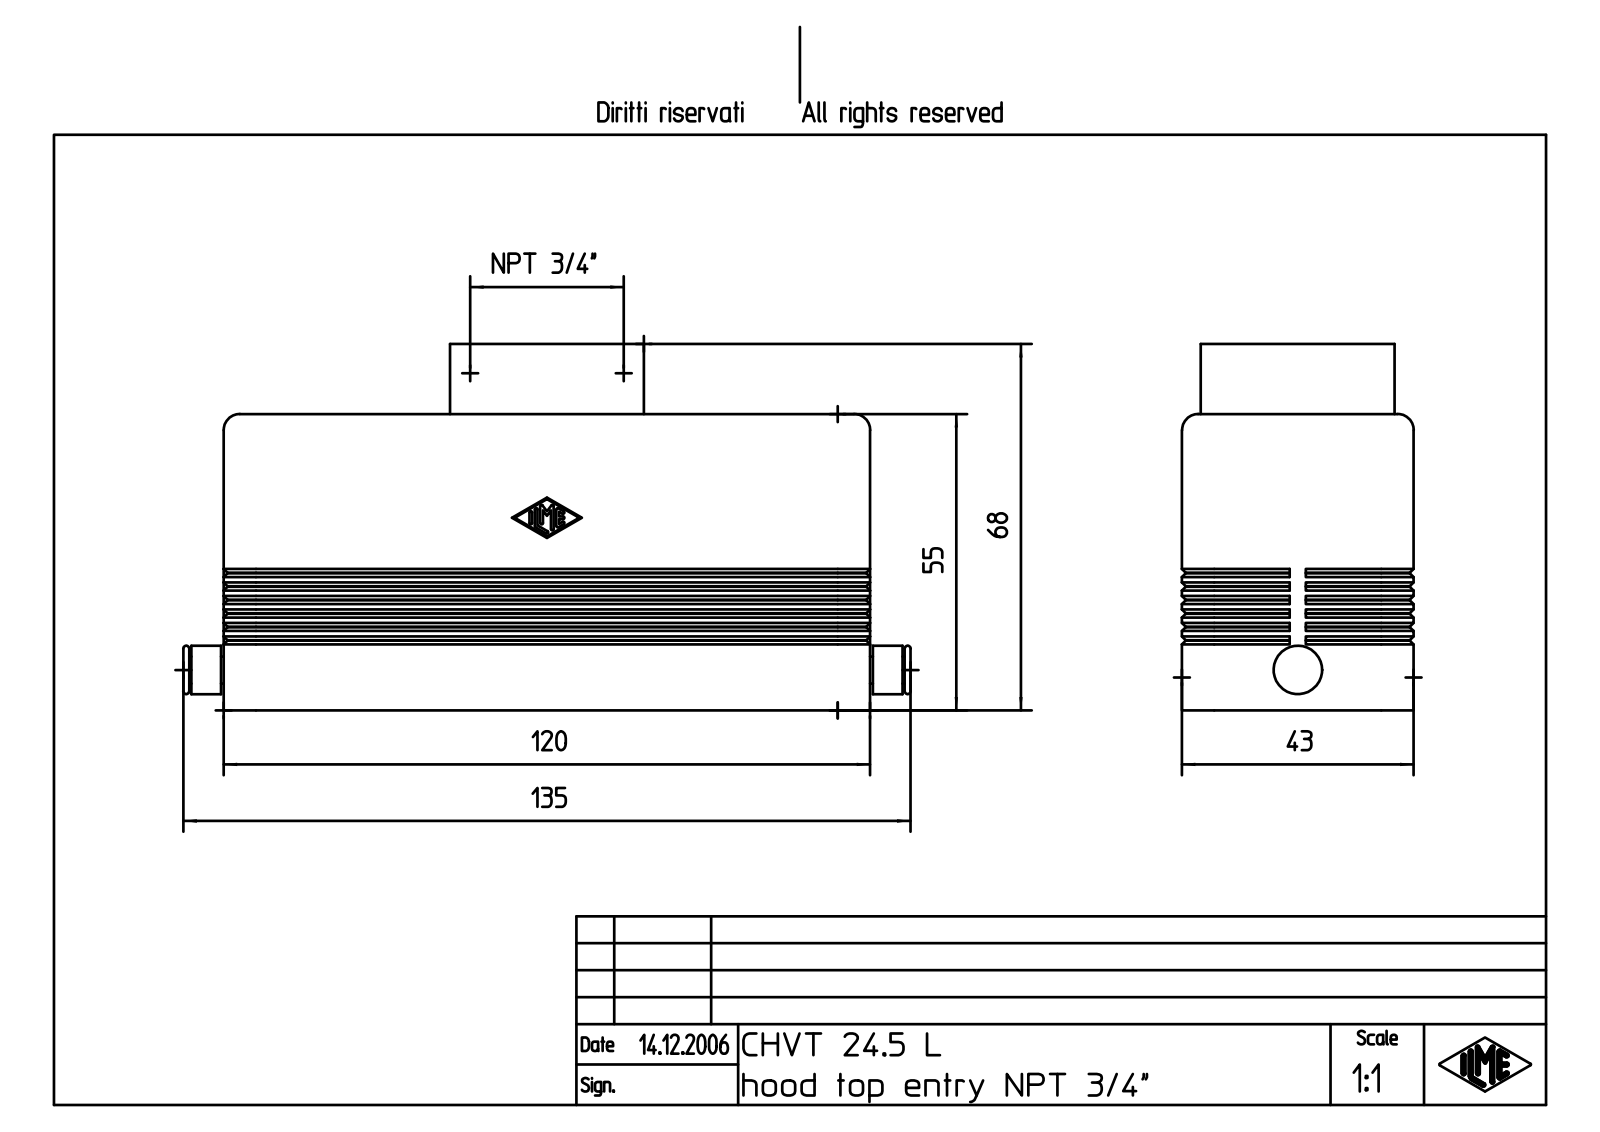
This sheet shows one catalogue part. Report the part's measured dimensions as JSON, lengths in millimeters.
{"part_name": "MSBO8121", "step_written_by": "Creo Elements/Direct Modeling 18.0B 02-Dec-2011 (C) Parametric Technology GmbH (AUTOMOTIVE_DESIGN)", "units": "millimeters", "bodies": {"solids": 1, "faces": 399, "planar": 223, "cylindrical": 110, "other": 66}, "overall_size": [135, 68, 43], "volume_mm3": 81228, "surface_area_mm2": 47115, "round_holes": [[4, 4], [2.46, 2], [2.46, 2]], "round_bosses_or_shafts": [[36, 1], [9, 1], [5, 1]], "partial_cylinders_radius": [[0.25, 14], [3, 8], [2, 4], [5.3, 4], [6, 4], [1.5, 1]], "face_to_face_distances": [3, 40, 37, 43, 11.5, 8.5, 1.77, 117, 5.3, 20], "hole_center_spacings": [27, 104, 107.45]}
